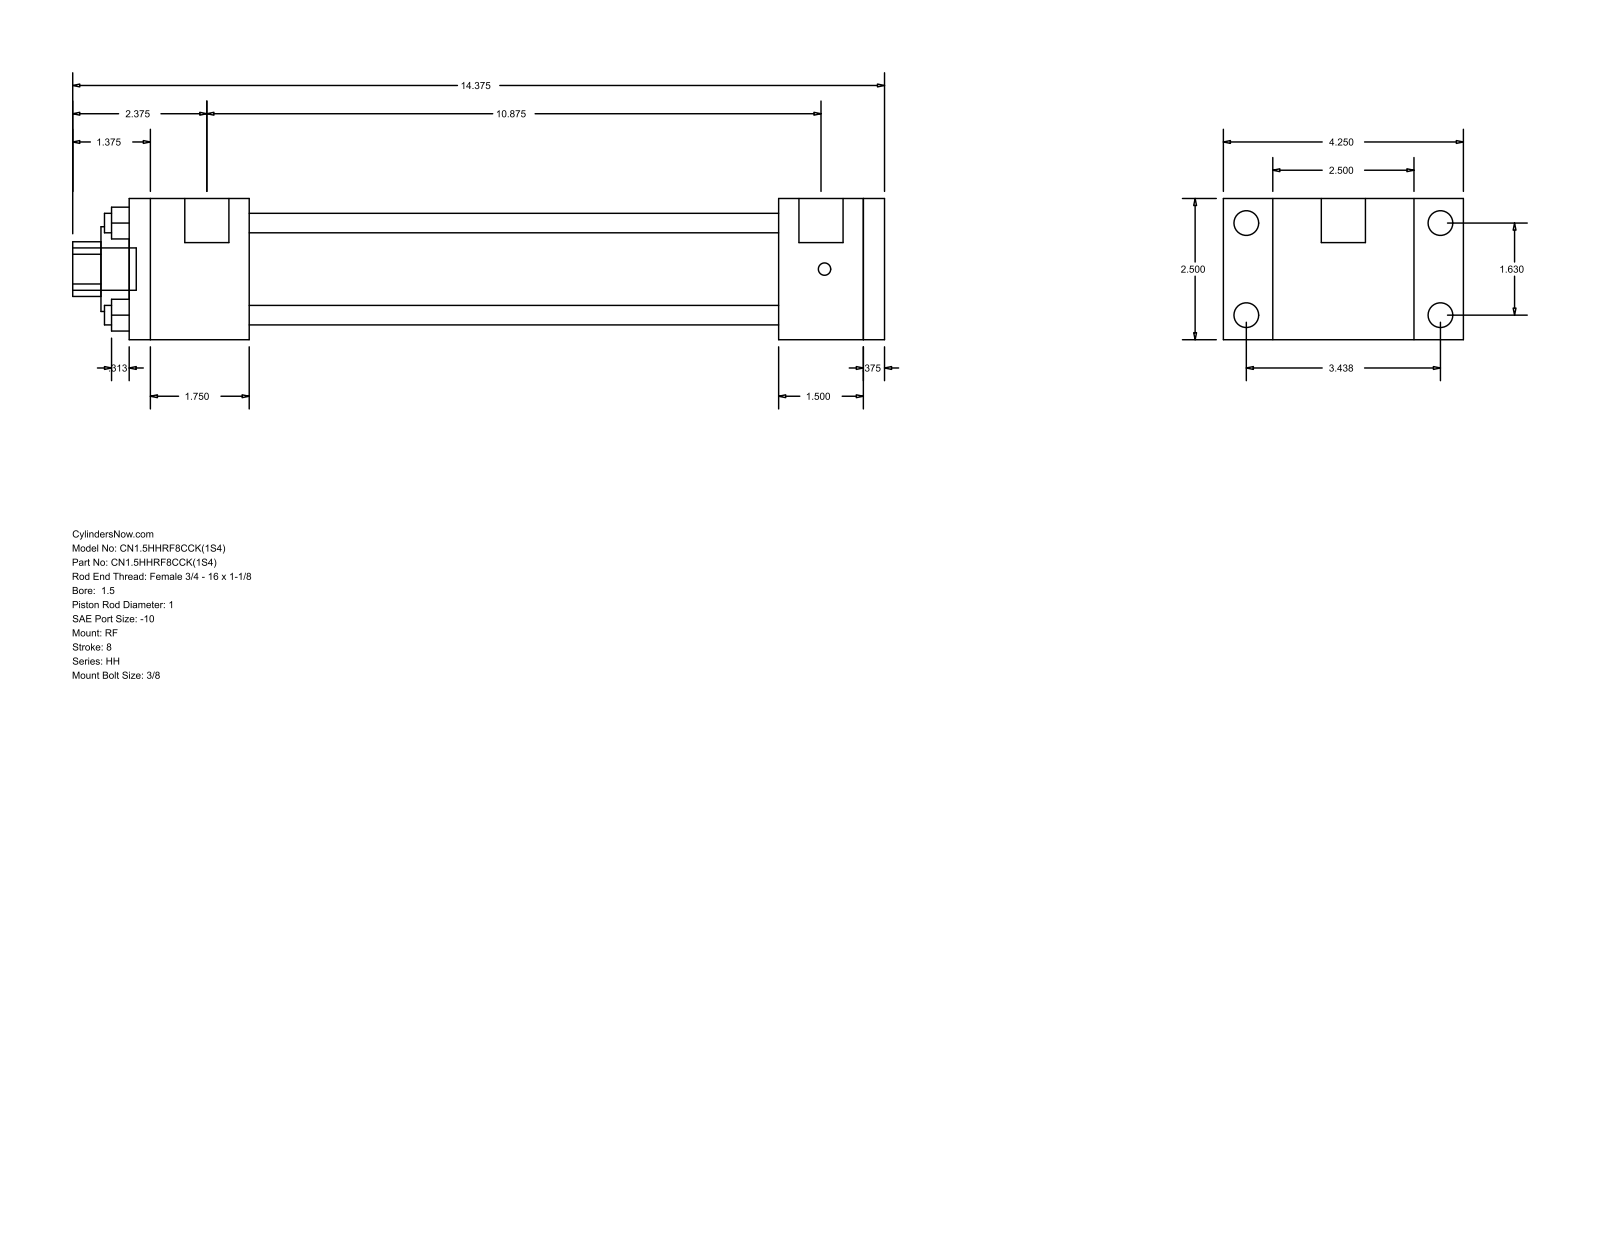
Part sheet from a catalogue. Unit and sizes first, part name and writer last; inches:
Units: inches
Overall size (bounding box): 14.375 × 4.25 × 2.5
Round holes (diameter × count): ⌀0.345 ×4, ⌀1 ×1, ⌀1.5 ×1, ⌀1.75 ×1
Round bosses / shafts (diameter × count): ⌀0.438 ×4, ⌀0.219 ×4, ⌀0.781 ×2, ⌀0.75 ×1
Partial cylindrical surfaces — rounded edges, fillets, slot ends (radius × count): R0.484 ×1
Main face-to-face distances: 2.5, 0.375, 9.375, 10.875, 11.25, 1.5, 1.875, 2.125, 11.5, 13
Hole centre spacings: 1.152, 1.63, 2.305
Bodies: 0 solids, 92 faces (64 planar, 28 cylindrical, 0 other)
Part name (STEP PRODUCT): HH_RF__0150_1
STEP written by: GSSL Pune (CONFIG_CONTROL_DESIGN)
